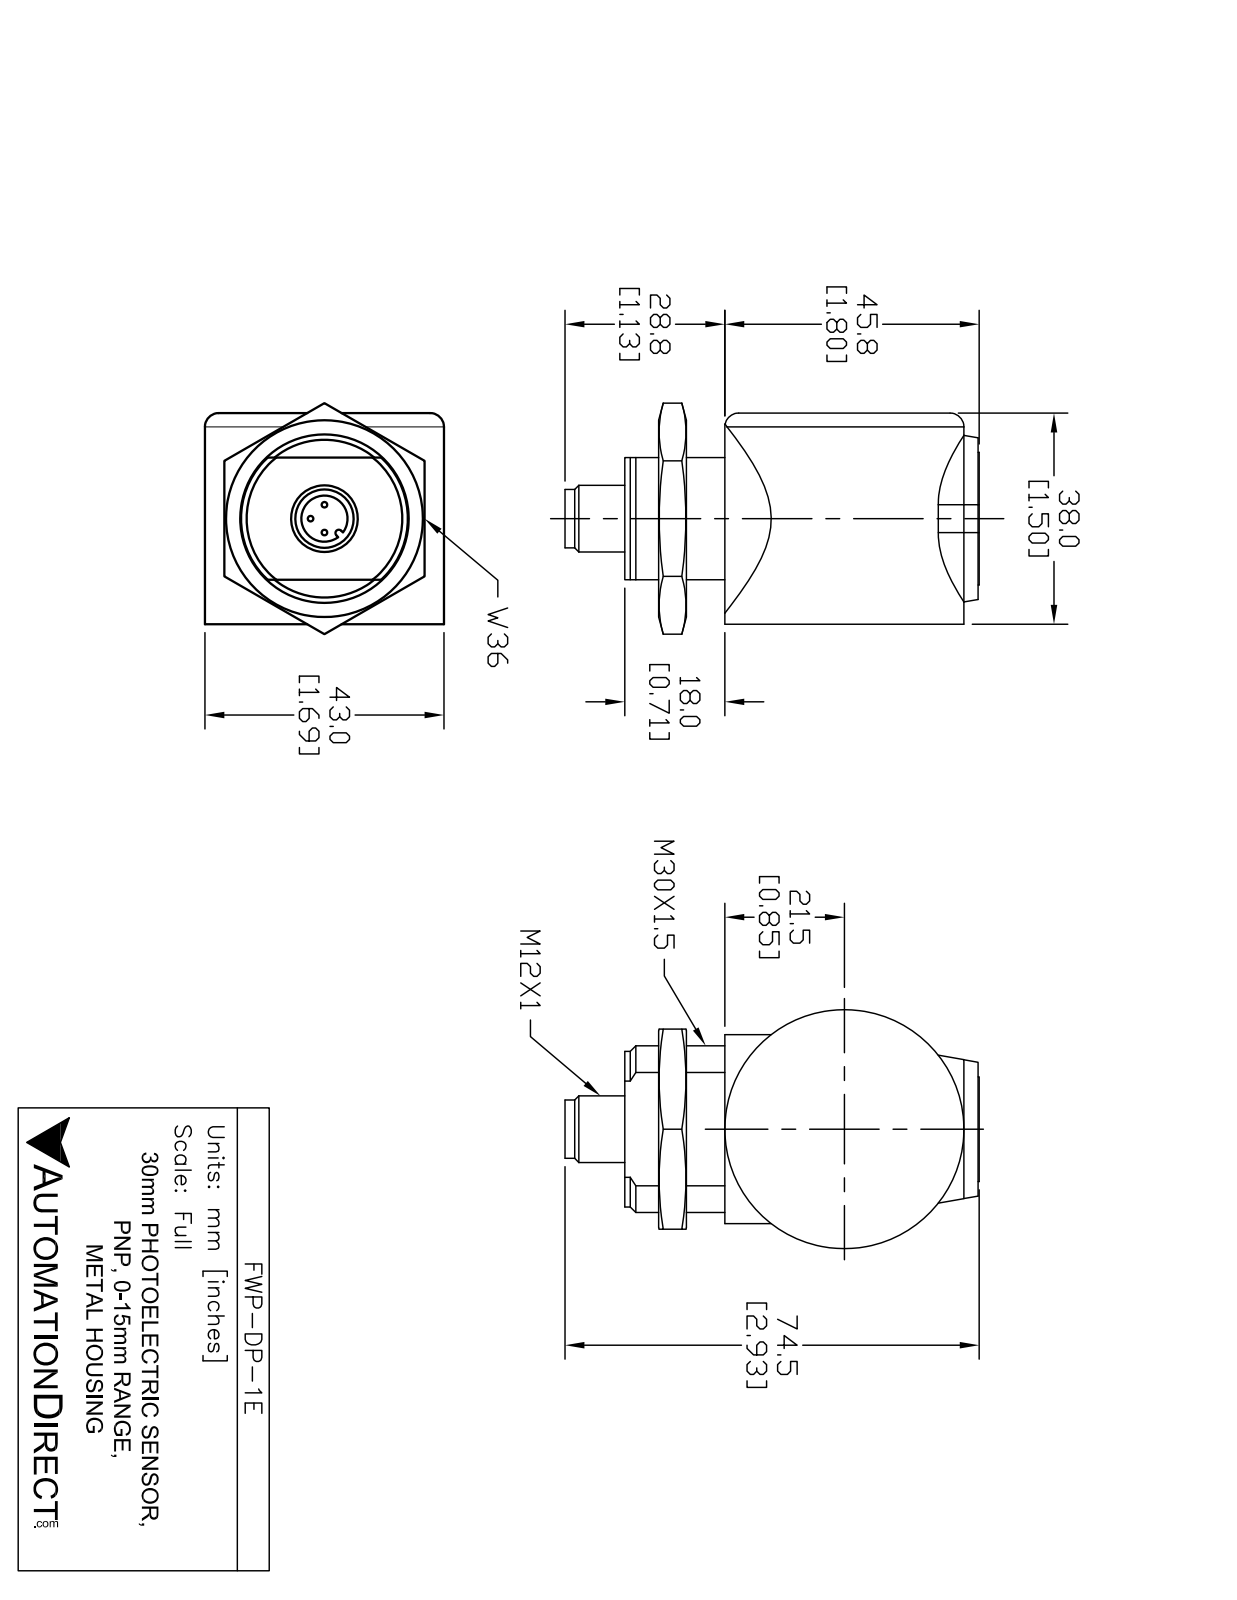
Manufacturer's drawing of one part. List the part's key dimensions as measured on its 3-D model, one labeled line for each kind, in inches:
Part name (STEP PRODUCT): FWP-DP-1E
STEP written by: SolidWorks 2013 (AUTOMOTIVE_DESIGN)
Units: inches
Bodies: 1 solid, 60 faces (29 planar, 24 cylindrical, 7 other)
Overall size (bounding box): 2.928 × 1.69 × 1.49
Volume: 4.417 in³ · Surface area: 19.34 in²
Round holes (diameter × count): ⌀0.315 ×1
Round bosses / shafts (diameter × count): ⌀0.04 ×3, ⌀1.69 ×1, ⌀0.47 ×1, ⌀0.39 ×1
Partial cylindrical surfaces — rounded edges, fillets, slot ends (radius × count): R0.64 ×2, R0.025 ×1, R0.545 ×1, R0.587 ×1
Main face-to-face distances: 1.49, 2.518, 0.11, 2.408, 0.3, 0.19, 2.218, 1.178, 0.312, 0.312
